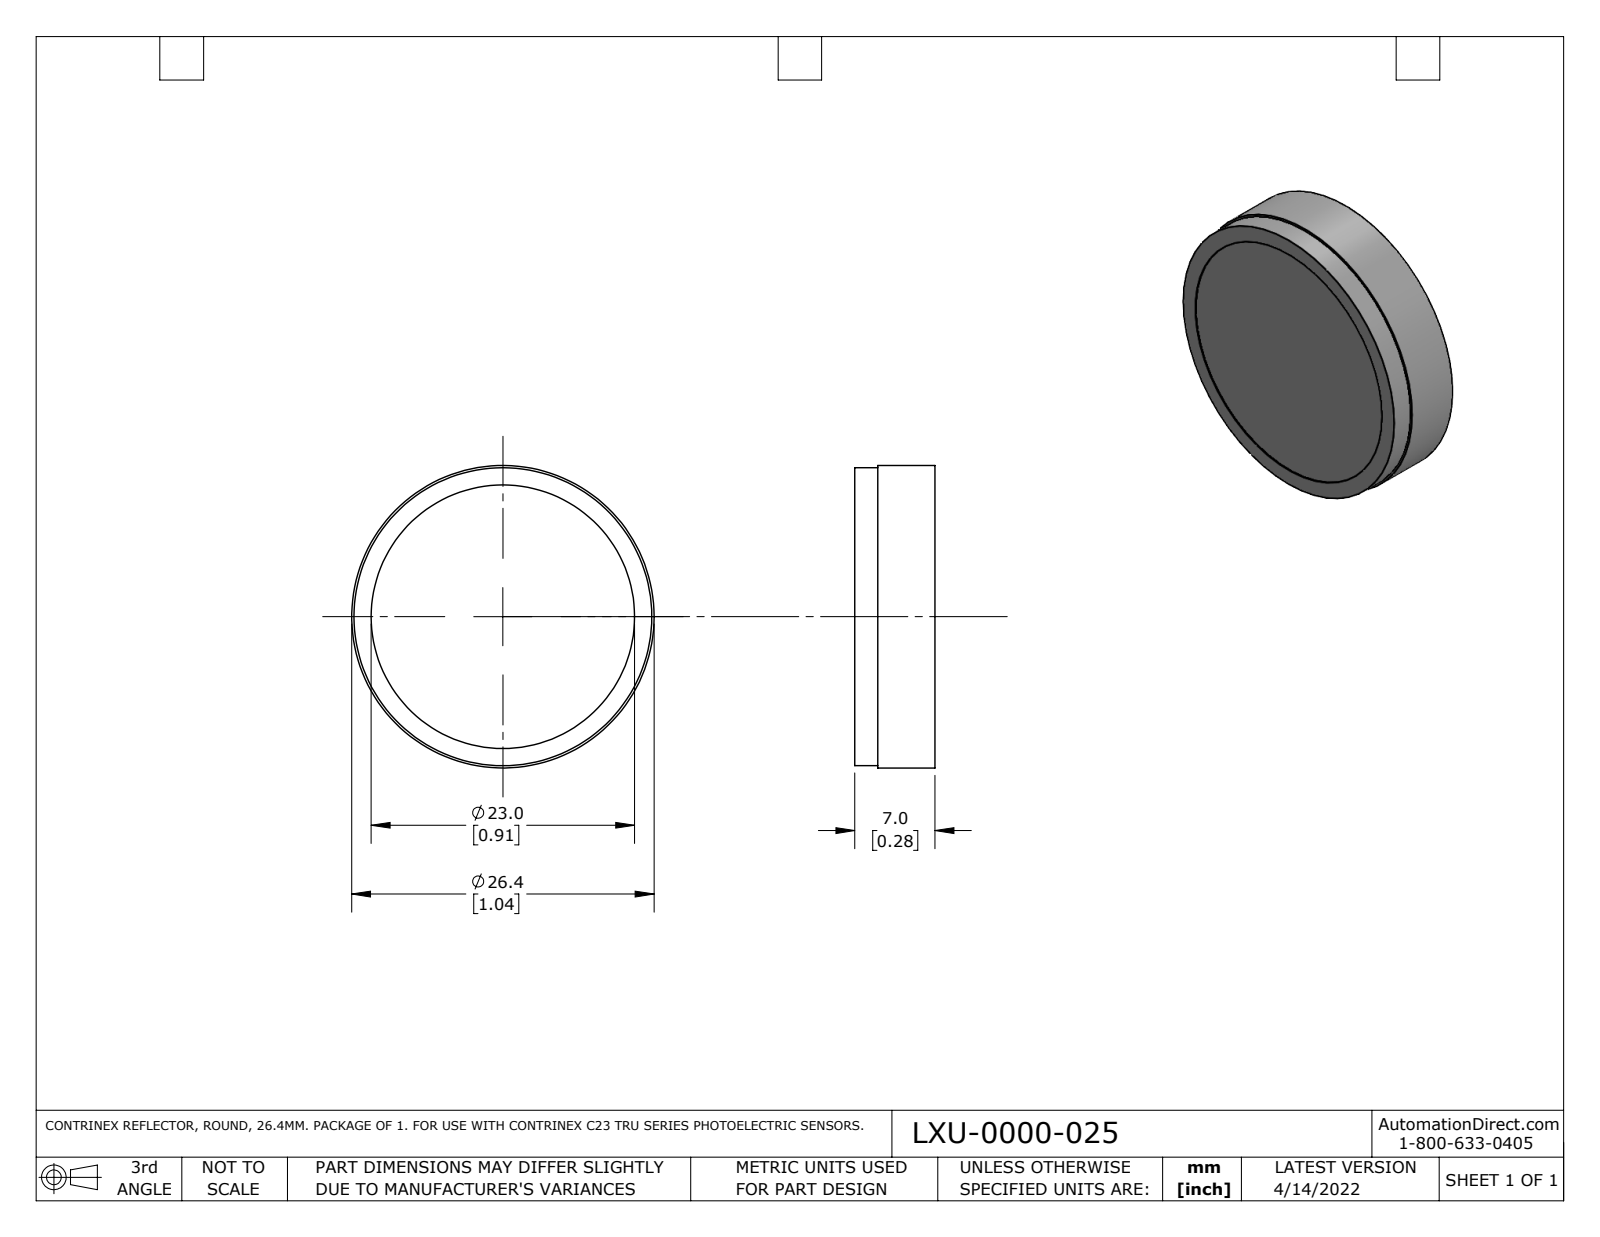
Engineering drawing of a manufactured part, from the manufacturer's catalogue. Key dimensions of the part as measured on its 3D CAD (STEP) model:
Part name (STEP PRODUCT): LXU-0000-025
STEP written by: PARTsolutions (AUTOMOTIVE_DESIGN)
Units: millimetres
Bodies: 1 solid, 7 faces (4 planar, 3 cylindrical, 0 other)
Overall size (bounding box): 26.4 × 26.4 × 7
Volume: 3 757 mm³ · Surface area: 1 680 mm²
Round holes (diameter × count): ⌀23 ×1
Round bosses / shafts (diameter × count): ⌀26.4 ×1, ⌀26 ×1
Main face-to-face distances: 6.9, 7, 5, 1.9, 2
